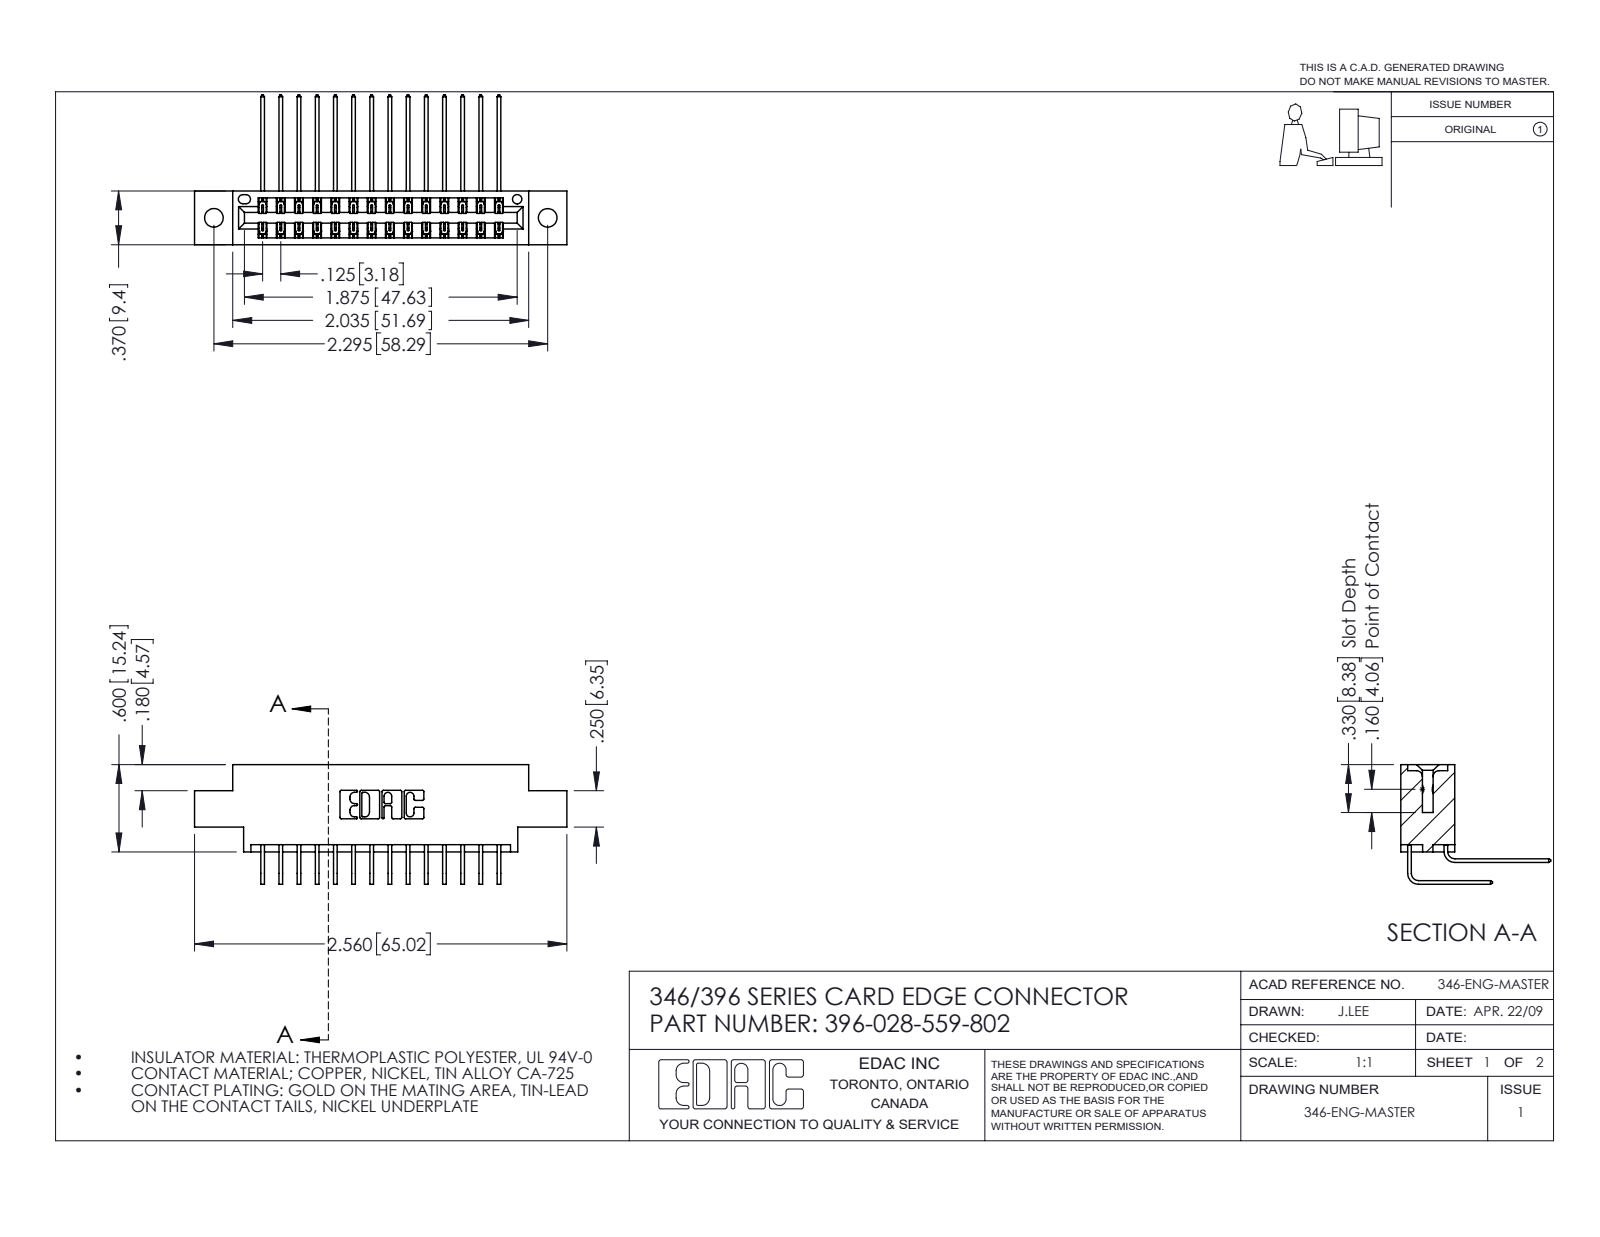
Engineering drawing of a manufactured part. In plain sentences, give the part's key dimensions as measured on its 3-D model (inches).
The part is named "346 Part_0.170 Offset - 0.128 Dia; 345-292-001_559 Tail - 2; 345-292-001_558 559 Tail - 1; 396-028-559-802". Its 3-D file was written by "SolidWorks 2016 (CONFIG_CONTROL_DESIGN)". It is 29 solids with 1638 faces: 1116 planar, 522 cylindrical and 0 other. Overall it measures 2.56 by 1.03 by 0.823 inches. Its volume is 0.372 cubic inches and its surface area 13.36 square inches. Round holes: 2 of diameter 0.128, 1 of diameter 0.064. Partial cylindrical surfaces (rounded edges, fillets, slot ends): 42 of radius 0.006, 22 of radius 0.01, 6 of radius 0.007, 6 of radius 0.031, 3 of radius 0.026, 2 of radius 0.014, 2 of radius 0.022, 2 of radius 0.024. The main face-to-face distances are 0.048, 0.322, 0.37, 0.25, 0.025, 0.072, 0.298, 0.275, 0.15, 0.148. The hole center spacings are 0.246, 2.089, 2.295.
